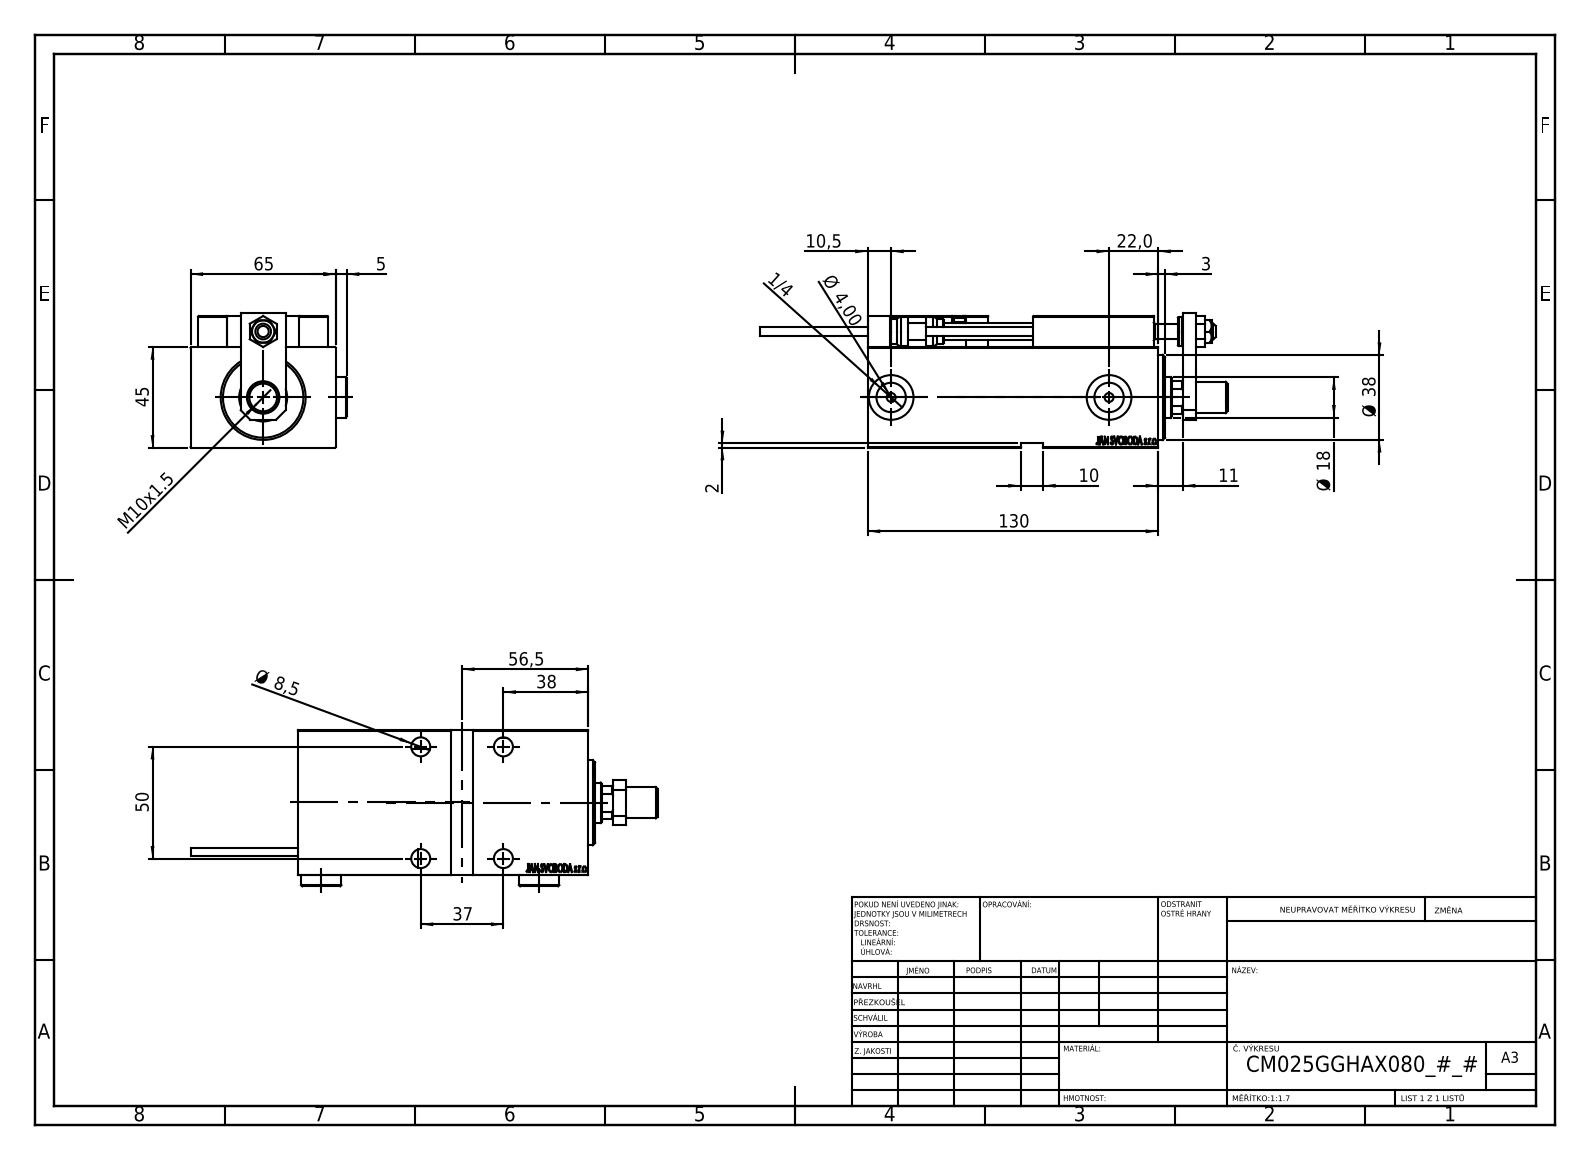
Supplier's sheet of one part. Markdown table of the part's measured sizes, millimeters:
| quantity | value |
| --- | --- |
| part name | NUT_D10; NUT_D12; Block; MAGNET (+8 more) |
| STEP written by | SolidWorks 2019 (CONFIG_CONTROL_DESIGN) |
| units | millimeters |
| bodies | 27 solids, 1347 faces (604 planar, 192 cylindrical, 551 other) |
| overall size | 209 × 172.4 × 60.5 |
| volume | 416 135 mm³ |
| surface area | 94 369 mm² |
| round holes (diameter × count) | 4 × 6, 8 × 5, 8.5 × 5, 3.2 × 4, 13.5 × 4, 5 × 2, 13.16 × 2, 20 × 2, 7 × 1, 14.5 × 1, 18 × 1, 21.5 × 1 |
| round bosses / shafts (diameter × count) | 18 × 2, 5 × 2, 3.8 × 2, 38 × 1, 14 × 1, 13 × 1, 12 × 1, 11 × 1 |
| partial cylindrical surfaces (radius × count) | 0.3 × 30, 3 × 2, 8.5 × 1 |
| main face-to-face distances | 45, 65, 14, 6, 59, 44.8, 58.8, 130, 141, 13 |
| hole center spacings | 11.37, 20, 29.59, 29.69, 34.44, 36.06, 37, 42.19 |
